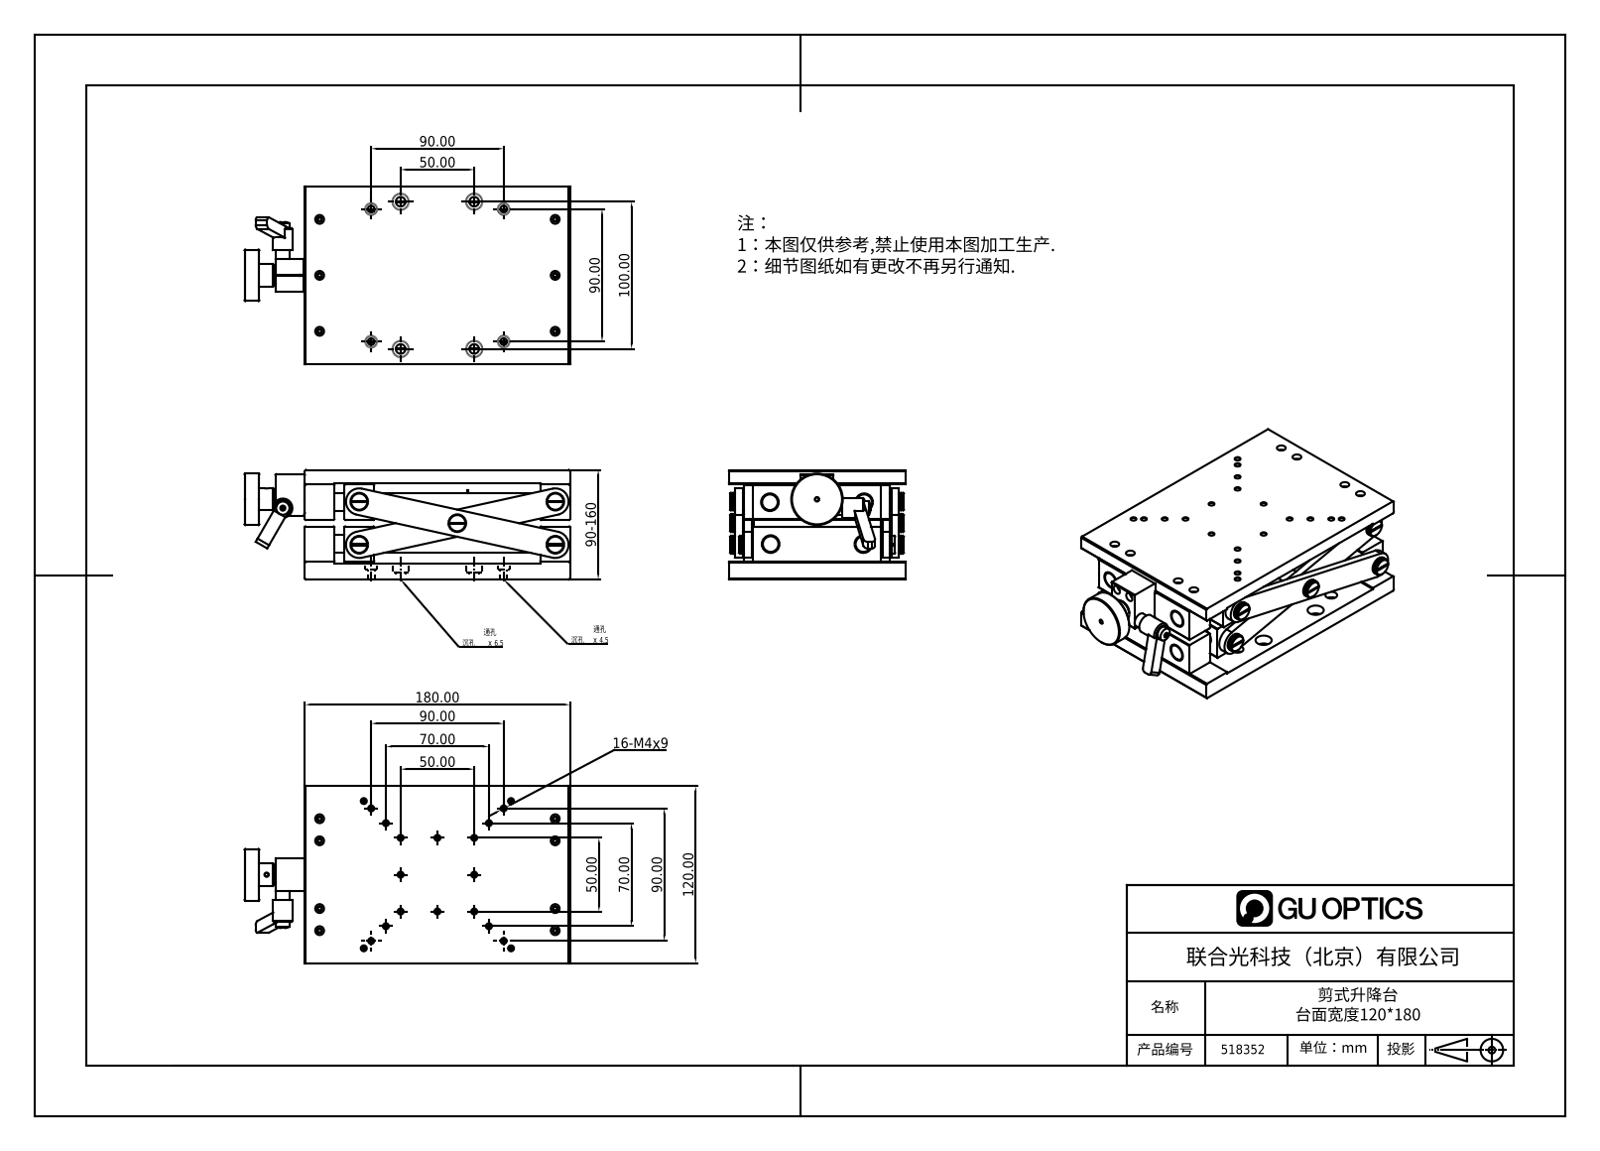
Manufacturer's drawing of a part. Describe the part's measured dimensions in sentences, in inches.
The part is named "518352". Its 3-D file was written by "SolidWorks 2020 (CONFIG_CONTROL_DESIGN)". It is 6 solids with 681 faces: 318 planar, 206 cylindrical and 157 other. Overall it measures 8.701 by 4.724 by 2.93 inches. Its volume is 51.93 cubic inches and its surface area 327.3 square inches. Round holes: 20 of diameter 0.128, 14 of diameter 0.097, 13 of diameter 0.236, 12 of diameter 0.138, 8 of diameter 0.097, 8 of diameter 0.315, 4 of diameter 0.177, 4 of diameter 0.256, 4 of diameter 0.433, 4 of diameter 0.472, 1 of diameter 0.157, 1 of diameter 0.768. Round bosses or shafts: 6 of diameter 0.472, 4 of diameter 0.157, 2 of diameter 0.512, 2 of diameter 0.315, 1 of diameter 1.378, 1 of diameter 0.748, 1 of diameter 0.709, 1 of diameter 0.591. Partial cylindrical surfaces (rounded edges, fillets, slot ends): 4 of radius 0.354, 1 of radius 0.079, 1 of radius 0.118. The main face-to-face distances are 0.433, 2.93, 0.354, 0.039, 2.575, 2.142, 2.496, 0.236, 0.787, 0.984. The hole center spacings are 2.201, 0.557, 0.984, 1.392, 1.433, 1.939, 2.395, 2.735.
